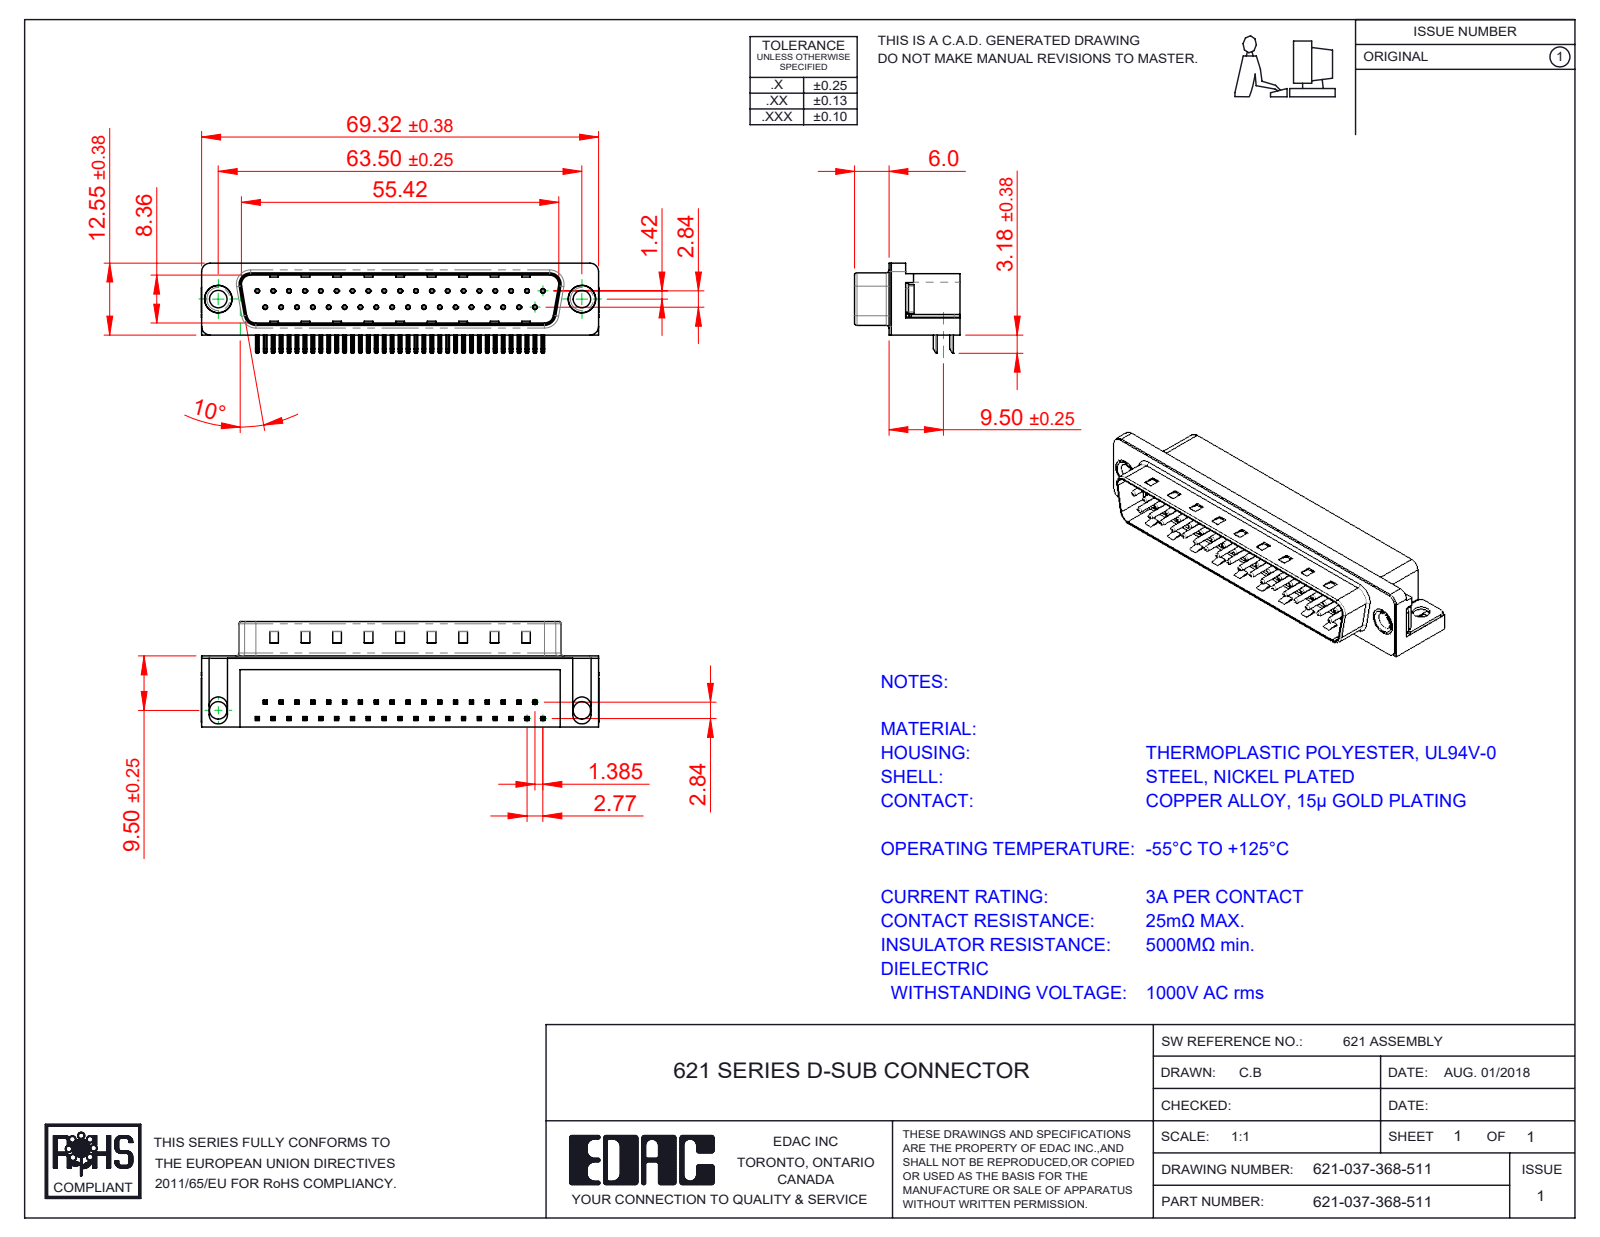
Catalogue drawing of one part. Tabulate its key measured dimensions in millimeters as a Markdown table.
| quantity | value |
| --- | --- |
| part name | 621 Housing_37 Socket; 621-037-368-511; 621 Thru Hole Board Mount; 621 Contact Bottom (+3 more) |
| STEP written by | SolidWorks 2016 (CONFIG_CONTROL_DESIGN) |
| units | millimeters |
| bodies | 43 solids, 3157 faces (2011 planar, 897 cylindrical, 249 other) |
| overall size | 69.4 × 18.4 × 15.73 |
| volume | 8 607 mm³ |
| surface area | 10 058 mm² |
| round holes (diameter × count) | 0.35 × 37, 0.8 × 37, 3.05 × 4, 4 × 2, 4.8 × 2, 5 × 2 |
| round bosses / shafts (diameter × count) | 0.75 × 37, 4.9 × 2, 4.75 × 2, 3.85 × 2 |
| partial cylindrical surfaces (radius × count) | 0.25 × 156, 0.12 × 74, 1 × 16, 0.5 × 9, 1.6 × 8, 1.5 × 7, 0.9 × 4, 2 × 4 |
| main face-to-face distances | 0.4, 12, 10.35, 8.76, 2.1, 1.7, 10.46, 10.86, 9, 12.4 |
| hole center spacings | 3.16, 2.77, 5.54, 8.31, 11.08, 13.85, 19.39, 22.16 |
